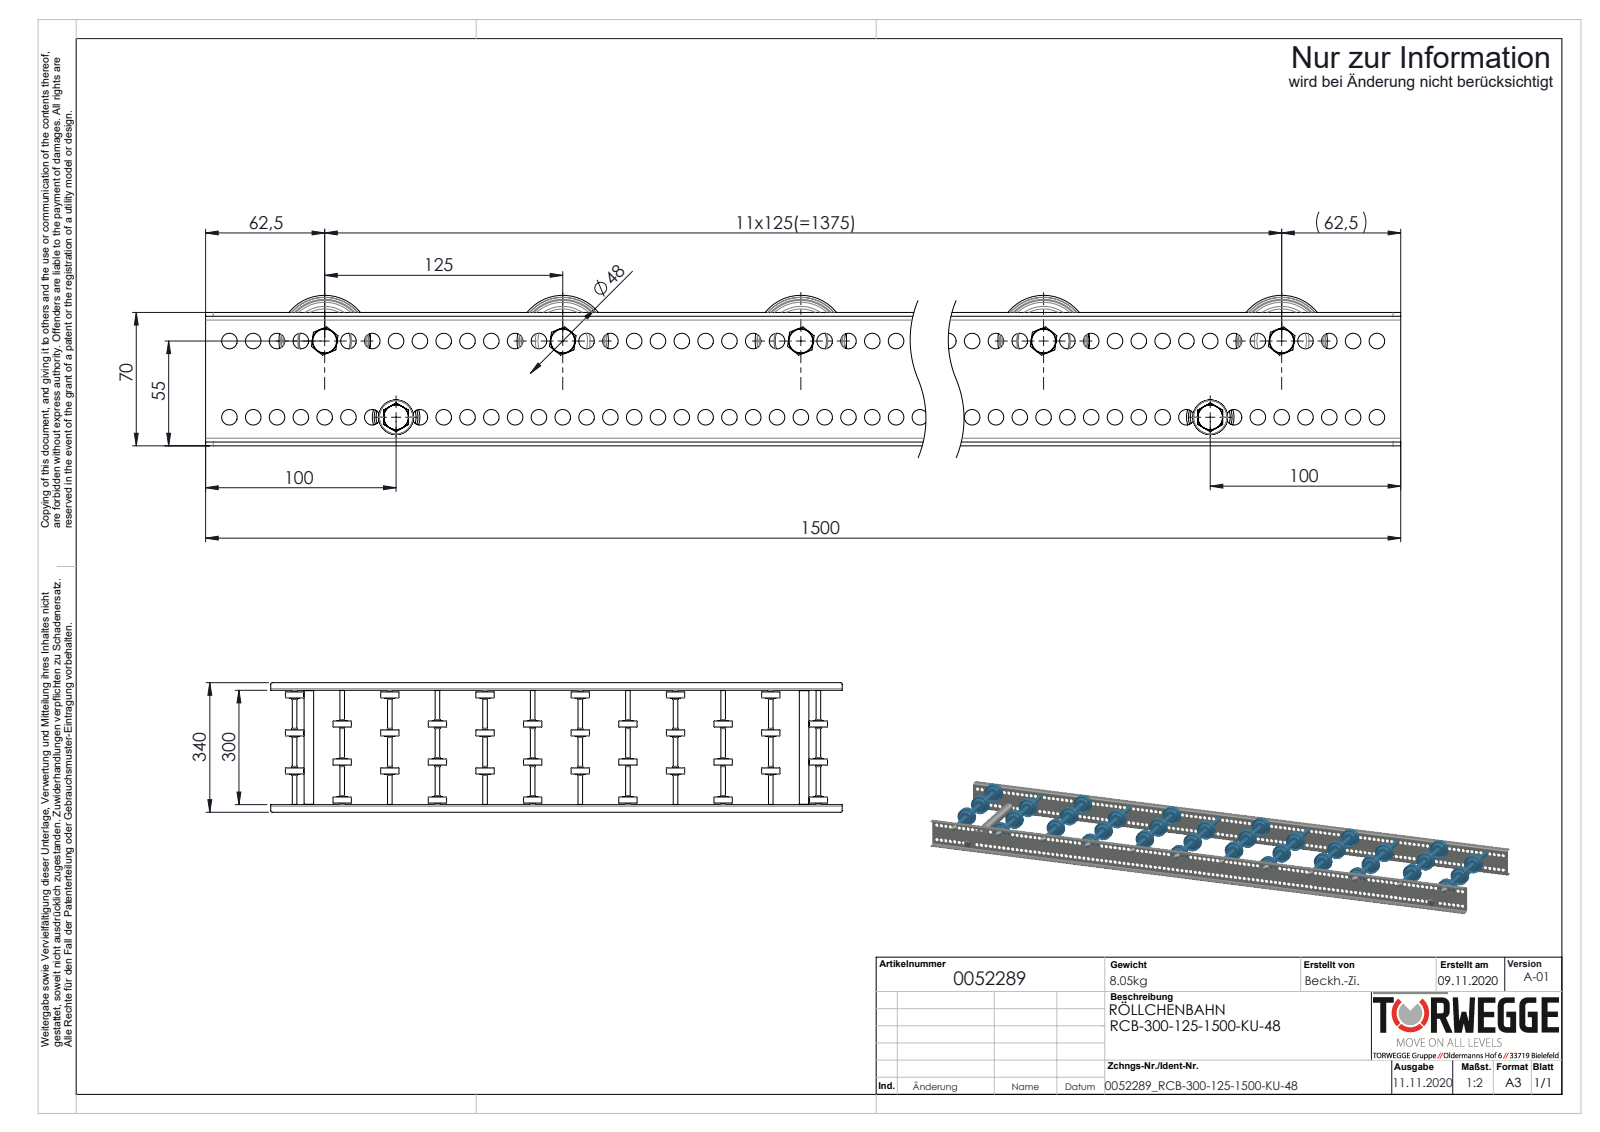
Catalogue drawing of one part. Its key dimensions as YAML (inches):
part_name: "Profil_LRB-20x70x20x2_KFG_S100201_U-PROFIL-20-70-20-2-LRB-L=1500; Röllchenachse-für-Konfiguration_EL300; S100994_Sperrzahnschraube_M08x16-8.8-A2K; Hutmutter_DIN_1587_M8 (+5 more)"
step_written_by: "SolidWorks 2020 (AUTOMOTIVE_DESIGN)"
units: inches
bodies: {solids: 120, faces: 4700, planar: 804, cylindrical: 1920, other: 1976}
overall_size: [59.055, 13.386, 3.11]
volume: 103.6
surface_area: 2108
round_holes:
  - {diameter: 0.323, count: 238}
  - {diameter: 0.262, count: 12}
  - {diameter: 0.38, count: 12}
  - {diameter: 0.539, count: 12}
  - {diameter: 0.268, count: 2}
  - {diameter: 0.827, count: 2}
round_bosses_or_shafts:
  - {diameter: 0.315, count: 14}
  - {diameter: 1.89, count: 12}
  - {diameter: 1.063, count: 12}
  - {diameter: 0.5, count: 12}
  - {diameter: 0.492, count: 12}
  - {diameter: 0.472, count: 12}
  - {diameter: 0.984, count: 2}
partial_cylinders:
  - {radius: 0.157, count: 8}
  - {radius: 0.079, count: 4}
face_to_face_distances: [0.079, 11.89, 2.677, 11.969, 11.811, 2.756, 2.598, 3.929, 0.642, 2.996]
hole_center_spacings: [0.492, 0.984, 1.476, 1.969, 2.461, 2.953, 3.445, 3.937]
